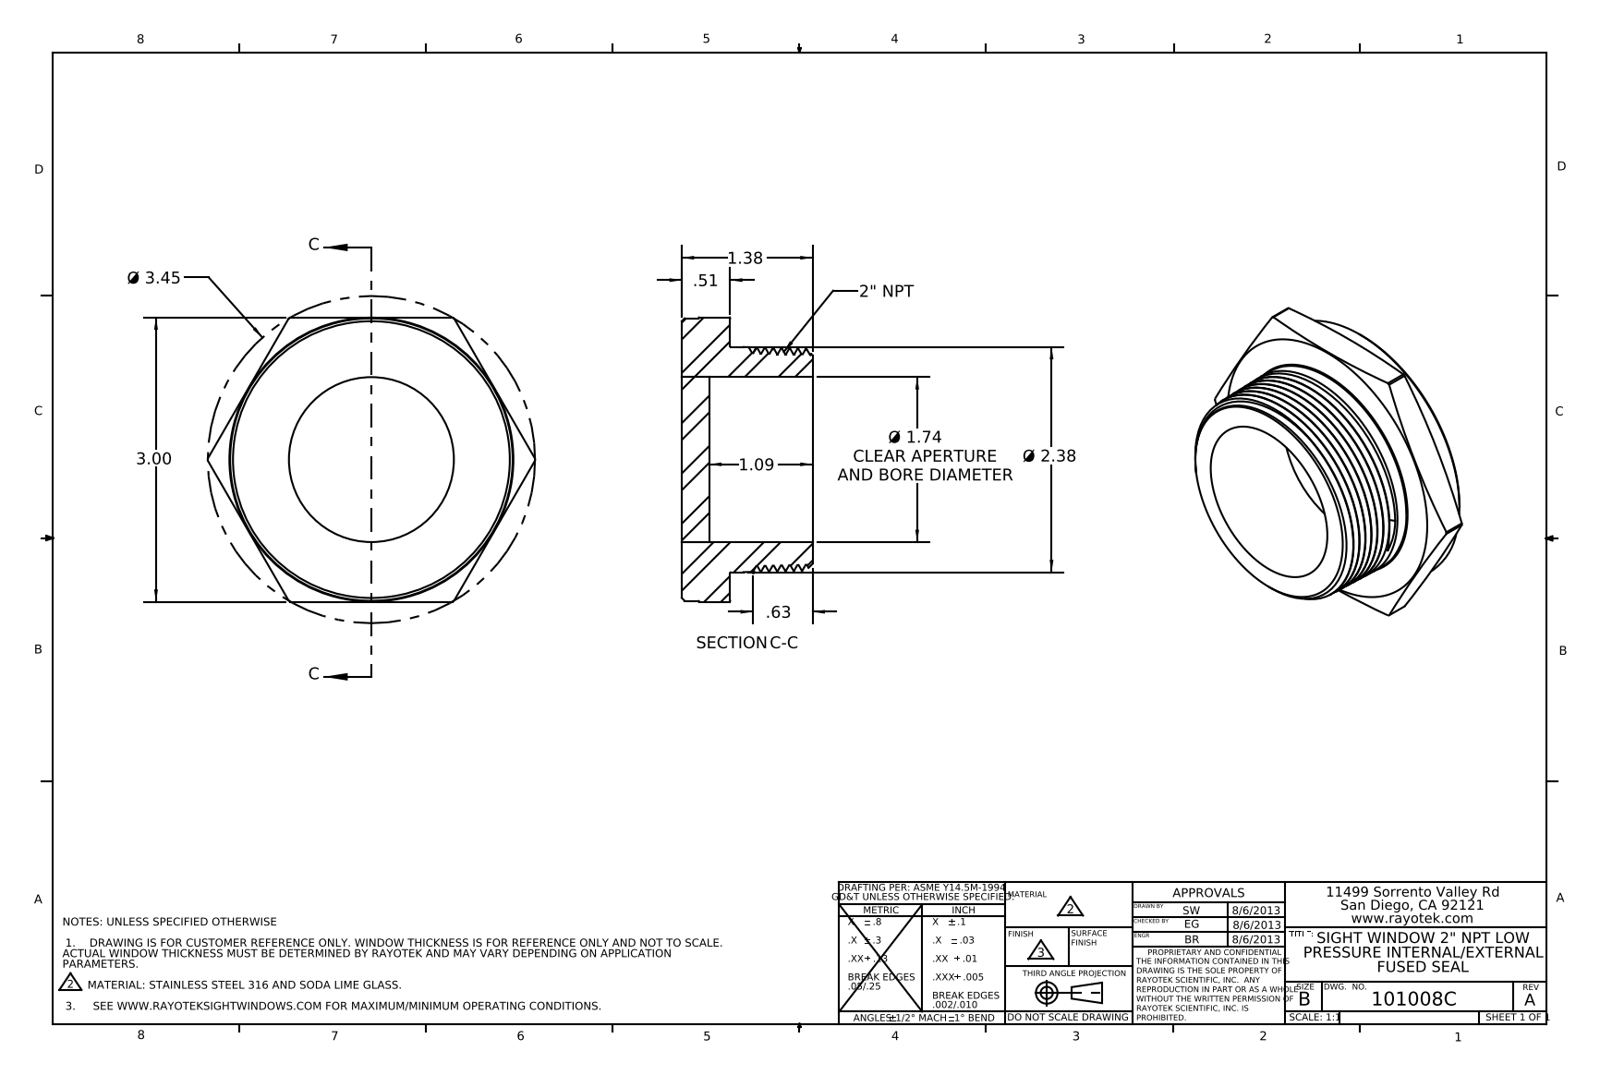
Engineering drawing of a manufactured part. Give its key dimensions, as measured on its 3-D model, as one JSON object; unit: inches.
{"part_name": "403008", "step_written_by": "SolidWorks 2012 (AUTOMOTIVE_DESIGN)", "units": "inches", "bodies": {"solids": 2, "faces": 60, "planar": 14, "cylindrical": 15, "other": 31}, "overall_size": [3.452, 3, 1.38], "volume_in3": 4.845, "surface_area_in2": 39.06, "round_holes": [[1.74, 1]], "round_bosses_or_shafts": [[2.98, 1], [2.375, 1]], "partial_cylinders_radius": [[1.726, 1]], "face_to_face_distances": [0.51, 0.29, 0.22, 3, 1.38, 1.09, 0.87]}
